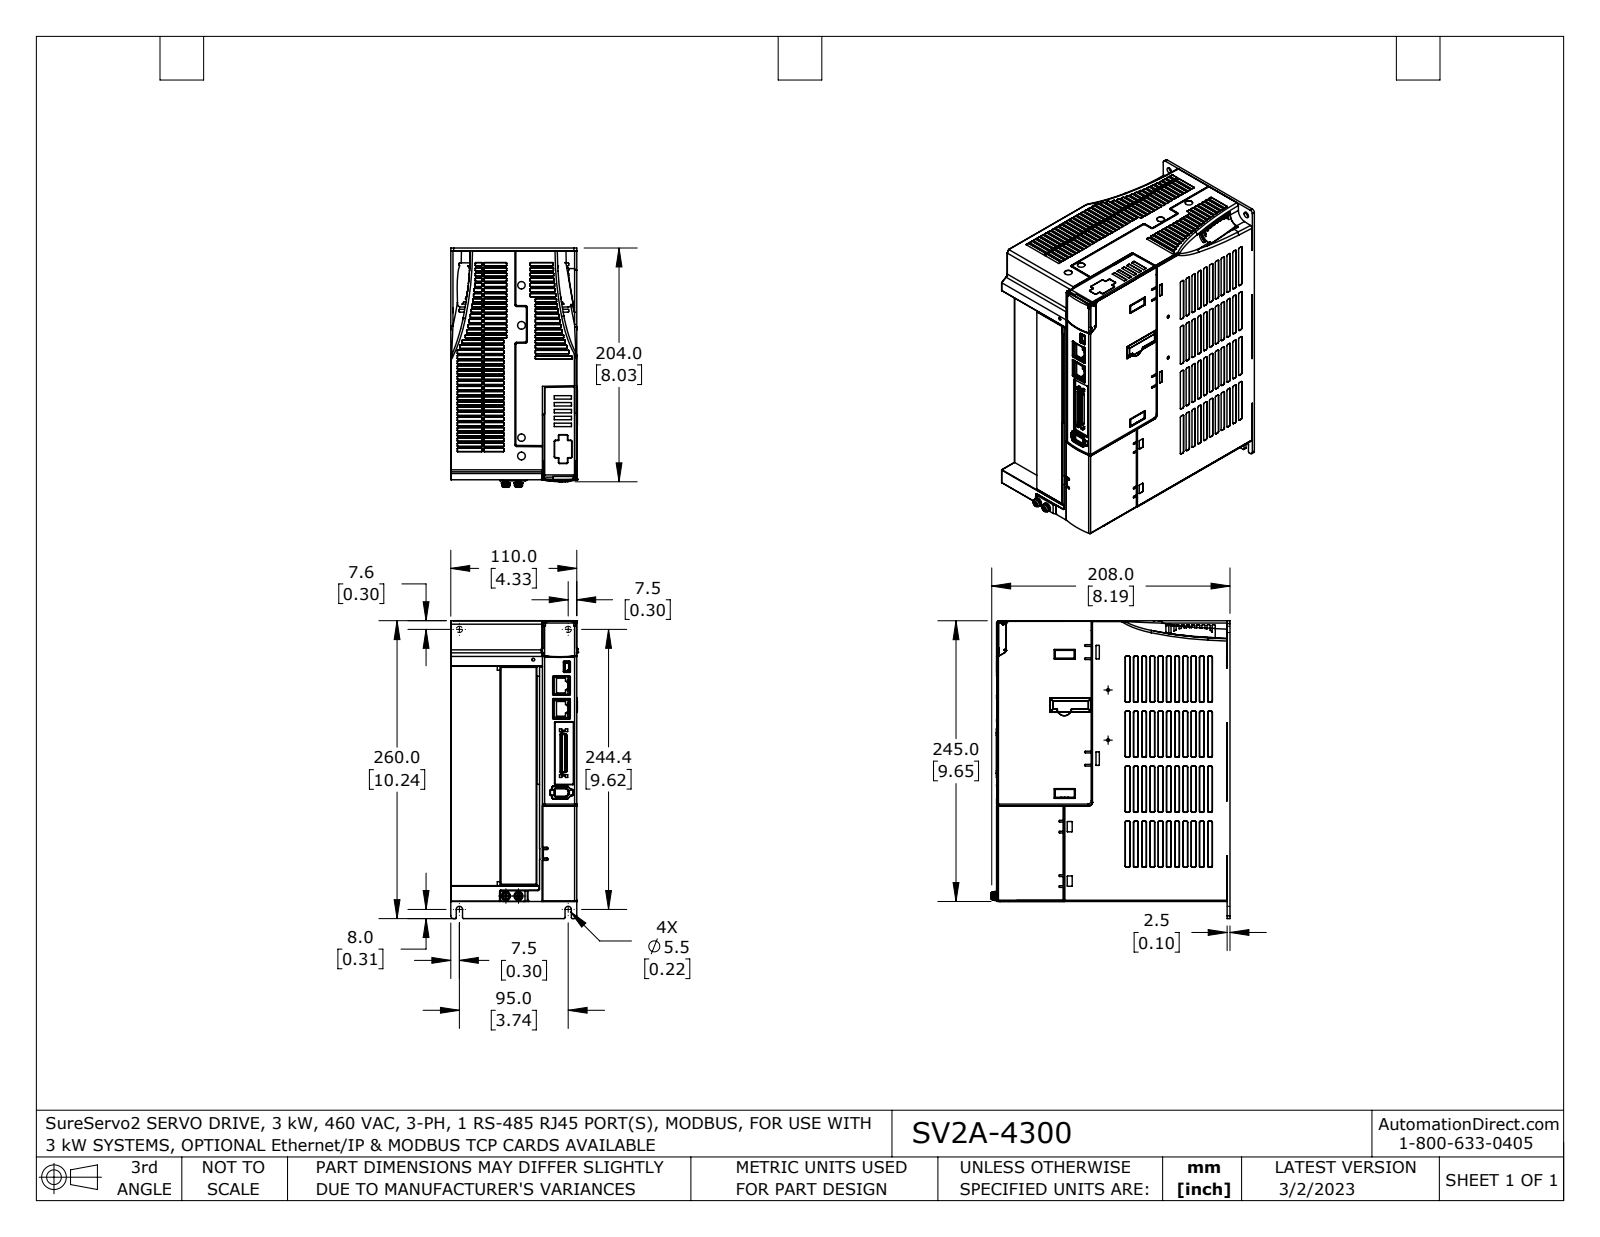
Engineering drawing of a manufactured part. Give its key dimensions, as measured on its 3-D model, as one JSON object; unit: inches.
{"part_name": "SV2A-4300-20200930 nc fxtredR1a ext1a -surfsa ext2 red2 ex4ADaa3cCac M1 coord", "step_written_by": "SolidWorks 2021 (AUTOMOTIVE_DESIGN)", "units": "inches", "bodies": {"solids": 2, "faces": 3570, "planar": 1871, "cylindrical": 1256, "other": 443}, "overall_size": [10.236, 8.223, 4.511], "volume_in3": 321.6, "surface_area_in2": 334.6, "round_holes": [[0.256, 4], [0.268, 4], [0.098, 3], [0.039, 2], [0.177, 2], [0.094, 1], [0.217, 1], [2.406, 1]], "round_bosses_or_shafts": [[0.307, 2], [0.276, 2], [0.256, 2], [0.157, 2], [0.193, 1], [0.118, 1]], "partial_cylinders_radius": [[0.039, 370], [0.02, 255], [0.012, 250], [0.024, 29], [0.004, 27], [0.031, 20], [0.008, 10], [0.03, 9]], "face_to_face_distances": [4.331, 9.644, 9.646, 4.328, 7.337, 4.33, 7.963, 4.327, 0.626, 9.643], "hole_center_spacings": [0.118, 0.167, 0.272, 0.302, 0.34, 0.433, 0.472, 0.63]}
